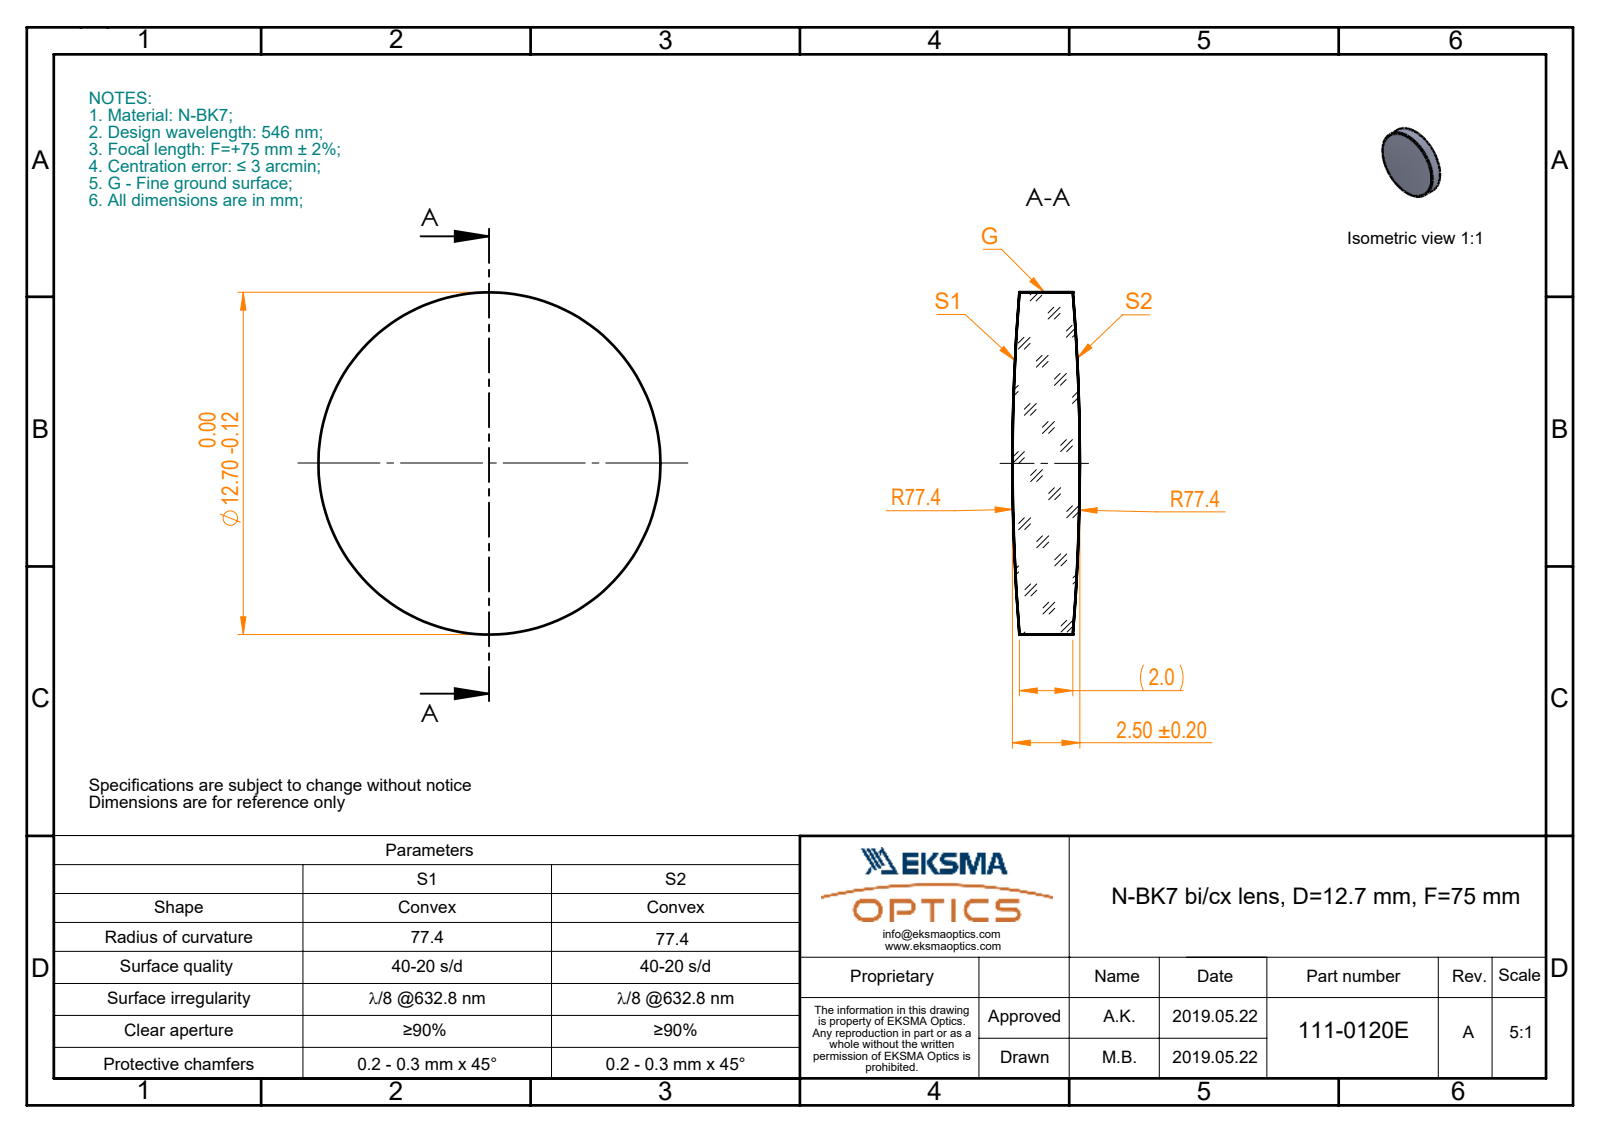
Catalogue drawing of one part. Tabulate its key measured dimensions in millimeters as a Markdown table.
| quantity | value |
| --- | --- |
| part name | 111-0120E BK7 bi-cx 12.7 F75 |
| STEP written by | SolidWorks 2017 (CONFIG_CONTROL_DESIGN) |
| units | millimeters |
| bodies | 1 solid, 6 faces (0 planar, 2 cylindrical, 4 other) |
| overall size | 12.7 × 12.7 × 2.5 |
| volume | 284 mm³ |
| surface area | 333 mm² |
| round bosses / shafts (diameter × count) | 12.7 × 1 |
